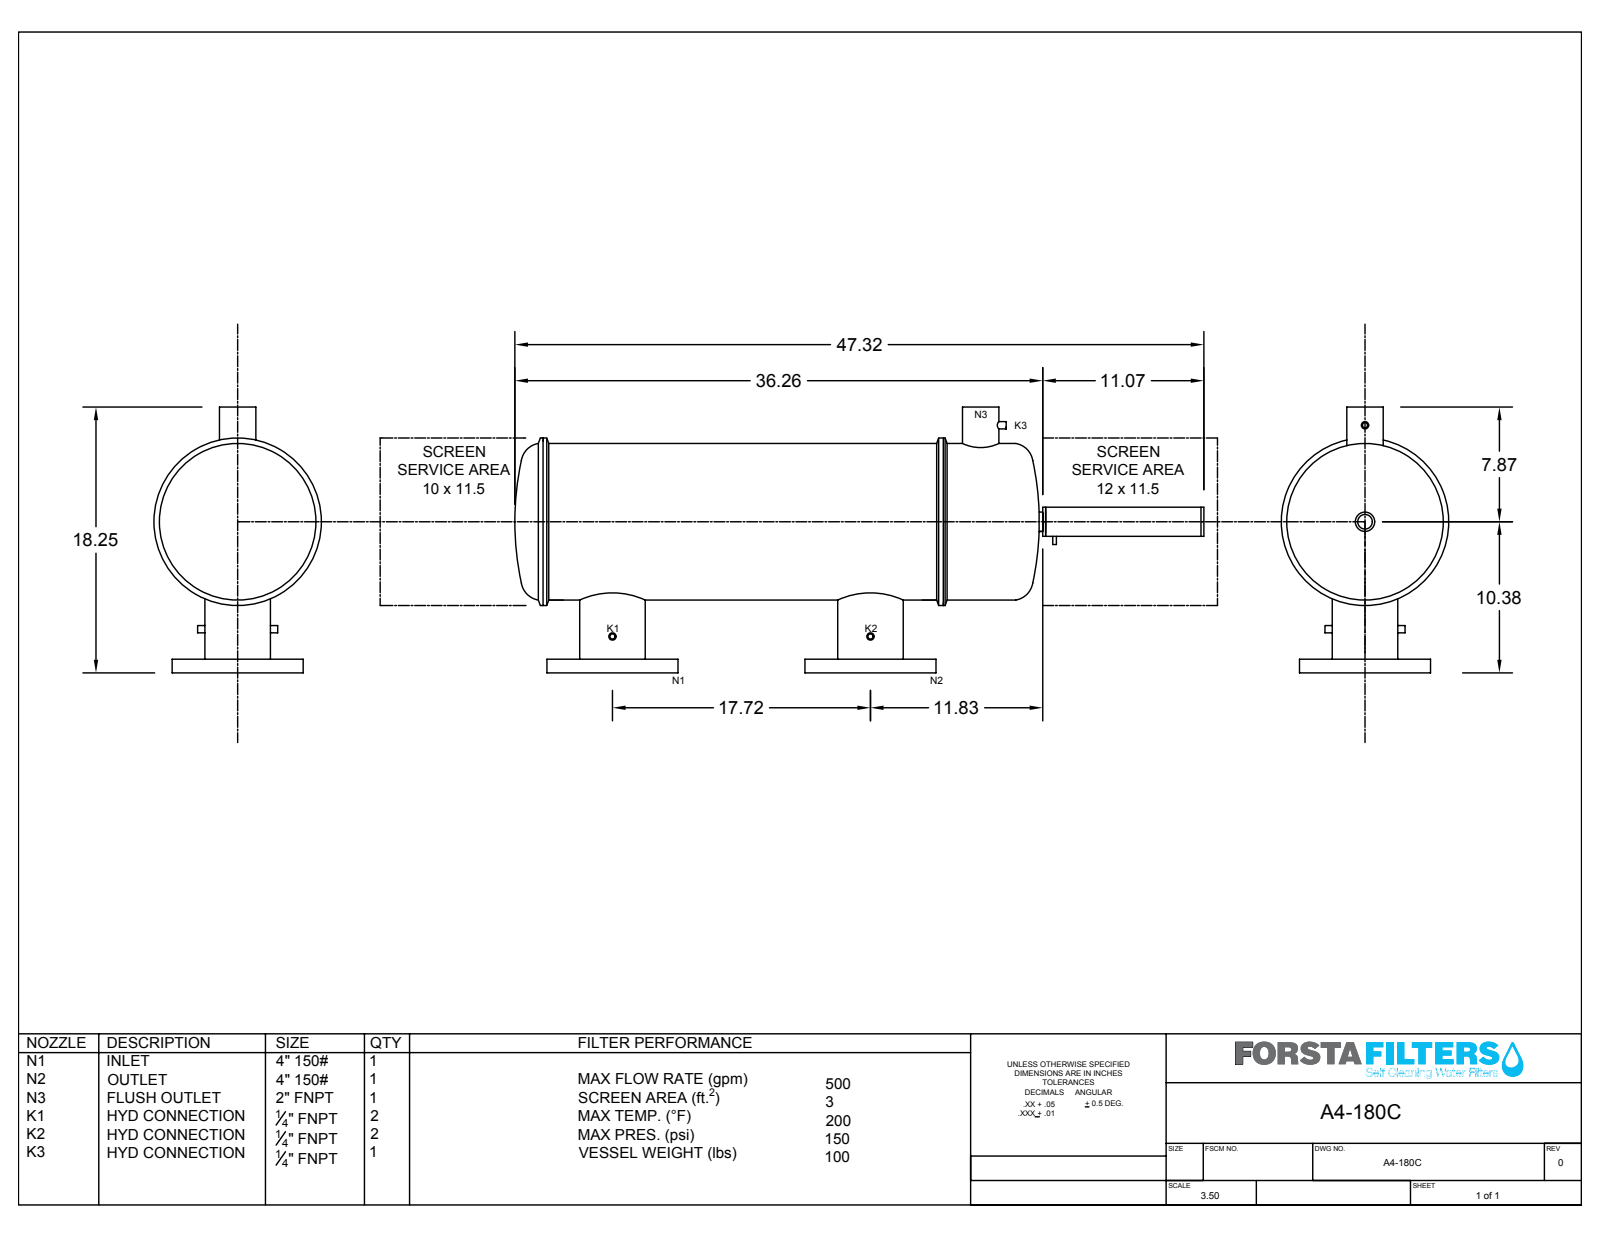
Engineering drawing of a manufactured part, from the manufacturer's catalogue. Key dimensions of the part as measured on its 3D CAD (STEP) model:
Part name (STEP PRODUCT): A4-180C
STEP written by: SolidWorks 2017 (CONFIG_CONTROL_DESIGN)
Units: inches
Bodies: 6 solids, 179 faces (41 planar, 94 cylindrical, 44 other)
Overall size (bounding box): 47.324 × 18.25 × 11.493
Volume: 410.4 in³ · Surface area: 3 366 in²
Round holes (diameter × count): ⌀0.75 ×16, ⌀0.25 ×3, ⌀1 ×2, ⌀4 ×2, ⌀0.093 ×1, ⌀0.936 ×1, ⌀2 ×1, ⌀10.35 ×1
Round bosses / shafts (diameter × count): ⌀0.644 ×3, ⌀9 ×2, ⌀4.394 ×2, ⌀11.493 ×1, ⌀10.743 ×1, ⌀2.394 ×1, ⌀1.993 ×1, ⌀0.25 ×1
Partial cylindrical surfaces — rounded edges, fillets, slot ends (radius × count): R1 ×2
Main face-to-face distances: 0.94, 0.25, 0.2, 10.867, 45.187, 34.519, 10.667, 45.387, 34.319, 11.067
Hole centre spacings: 2.87, 3.75, 5.303, 6.929, 13.8, 7.5, 9.129, 10.16
